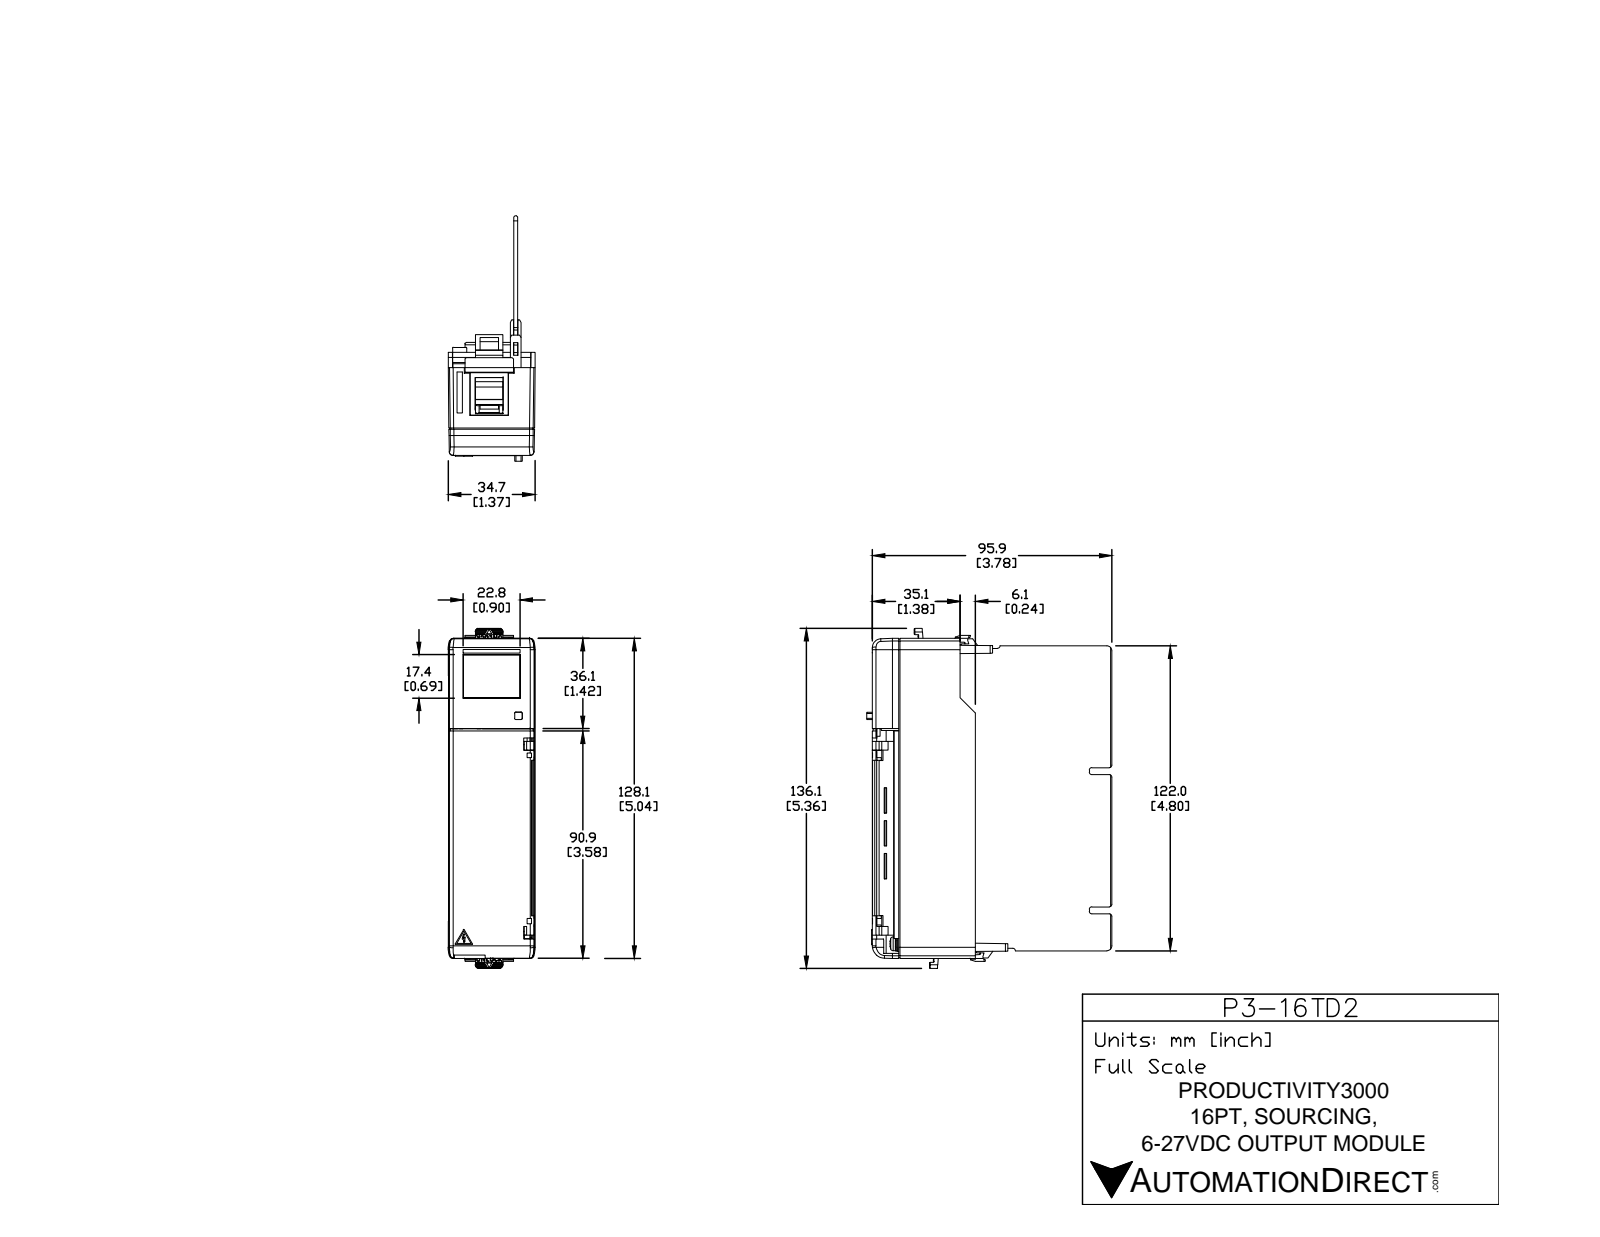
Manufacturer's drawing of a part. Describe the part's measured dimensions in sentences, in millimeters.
The part is named "P3-16TD2". Its 3-D file was written by "SolidWorks 2009 (CONFIG_CONTROL_DESIGN)". It is 1 solid with 3804 faces: 2821 planar, 737 cylindrical and 246 other. Overall it measures 136.08 by 96.19 by 34.8 millimeters. Its volume is 101 334 cubic millimeters and its surface area 75 406 square millimeters. Round holes: 22 of diameter 3.2, 2 of diameter 5, 1 of diameter 1.8. Round bosses or shafts: 22 of diameter 5.5, 22 of diameter 3, 20 of diameter 2.4, 2 of diameter 5.6, 2 of diameter 2.2, 2 of diameter 2, 1 of diameter 1.5. Partial cylindrical surfaces (rounded edges, fillets, slot ends): 91 of radius 0.5, 33 of radius 1, 29 of radius 0.3, 22 of radius 1.67, 13 of radius 1.5, 6 of radius 2, 5 of radius 0.2, 4 of radius 0.1. The main face-to-face distances are 1.6, 1.7, 28.23, 26.53, 32.56, 22.2, 2.2, 7.9, 6.8, 5.32. The hole center spacings are 8.68, 7.62, 13.84, 15.24, 20.59, 22.86, 27.79, 30.48.
